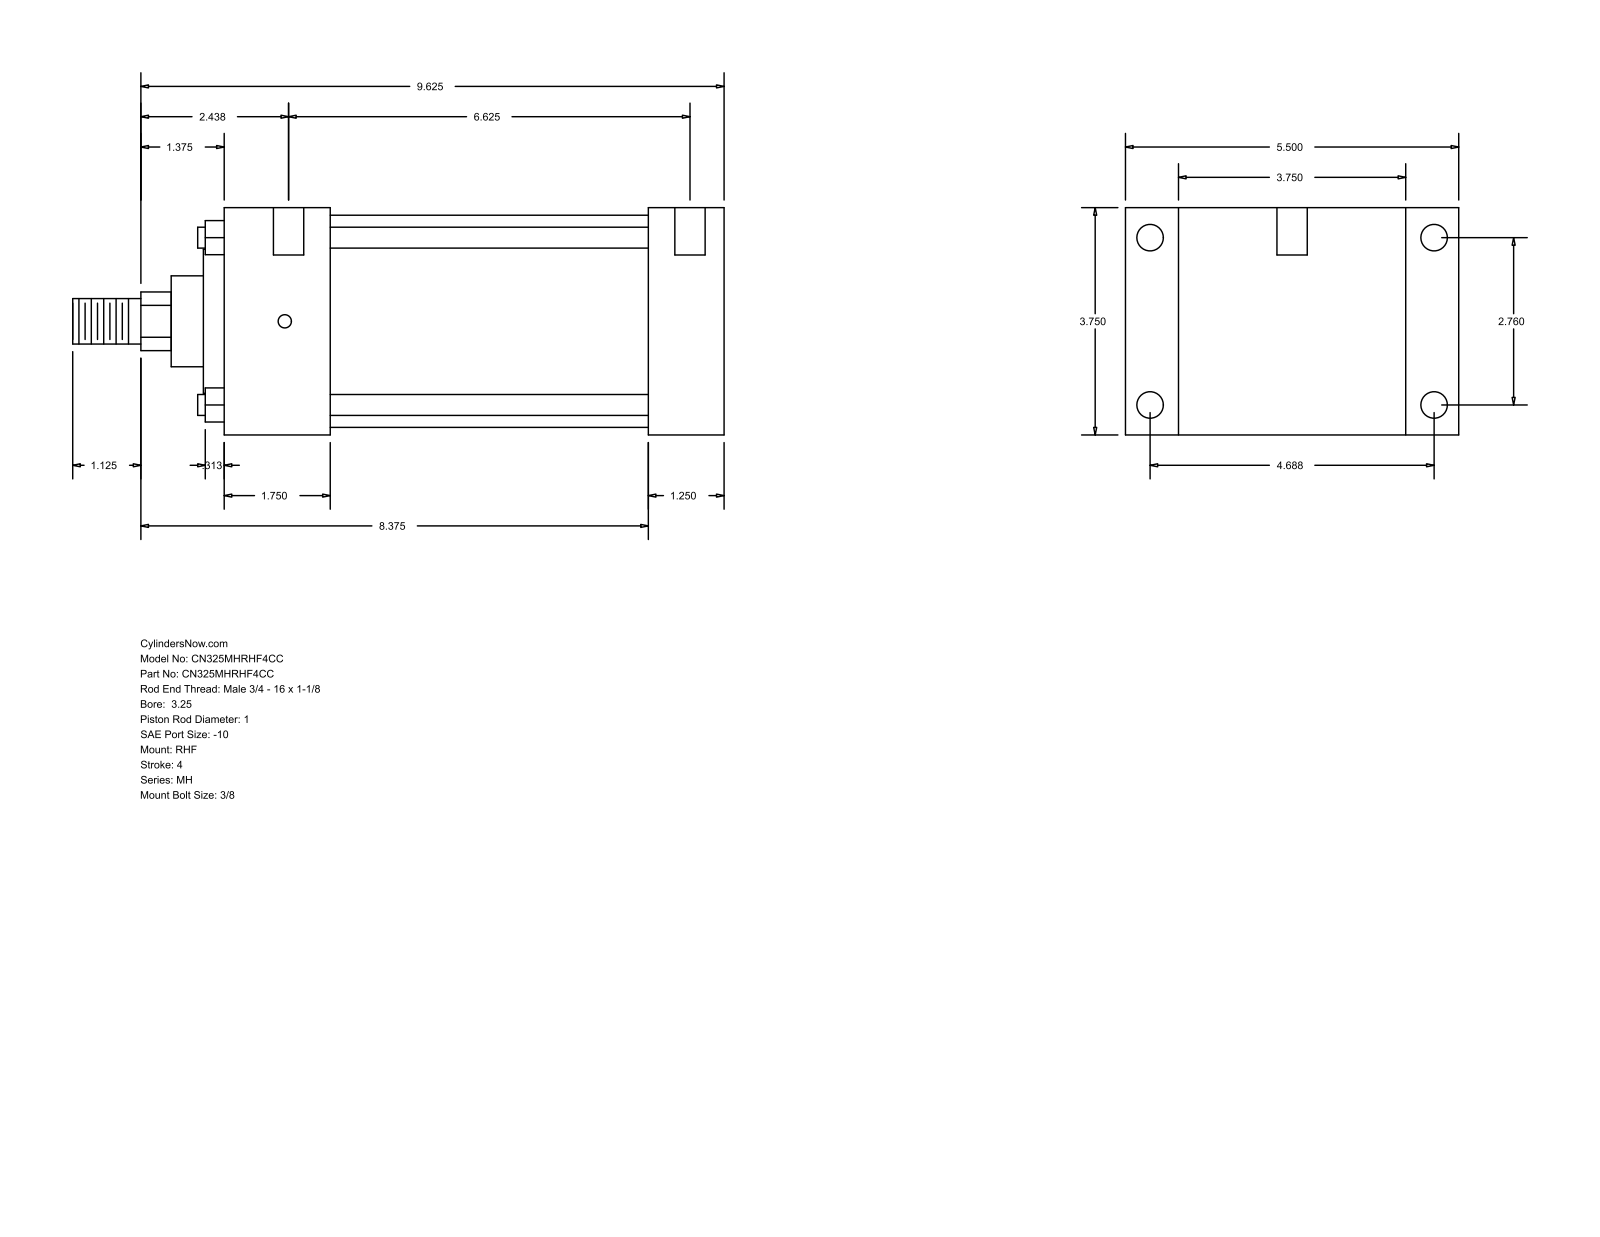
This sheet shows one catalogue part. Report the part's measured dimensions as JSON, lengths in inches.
{"part_name": "MH_RHF__0325_1", "step_written_by": "GSSL Pune (CONFIG_CONTROL_DESIGN)", "units": "inches", "bodies": {"solids": 0, "faces": 90, "planar": 61, "cylindrical": 29, "other": 0}, "overall_size": [10.75, 5.5, 3.75], "round_holes": [[0.219, 4], [0.438, 4], [0.5, 2]], "round_bosses_or_shafts": [[0.345, 4], [3.5, 1], [2.375, 1], [1.5, 1], [1, 1], [0.75, 1]], "partial_cylinders_radius": [[0.484, 1]], "face_to_face_distances": [3.75, 1.25, 0.875, 4.625, 7, 8.25, 5.5, 1.75, 5.25, 6.5], "hole_center_spacings": [2.76, 4.687, 5.439, 6.875, 0.062, 0.187, 6.625, 6.687]}
